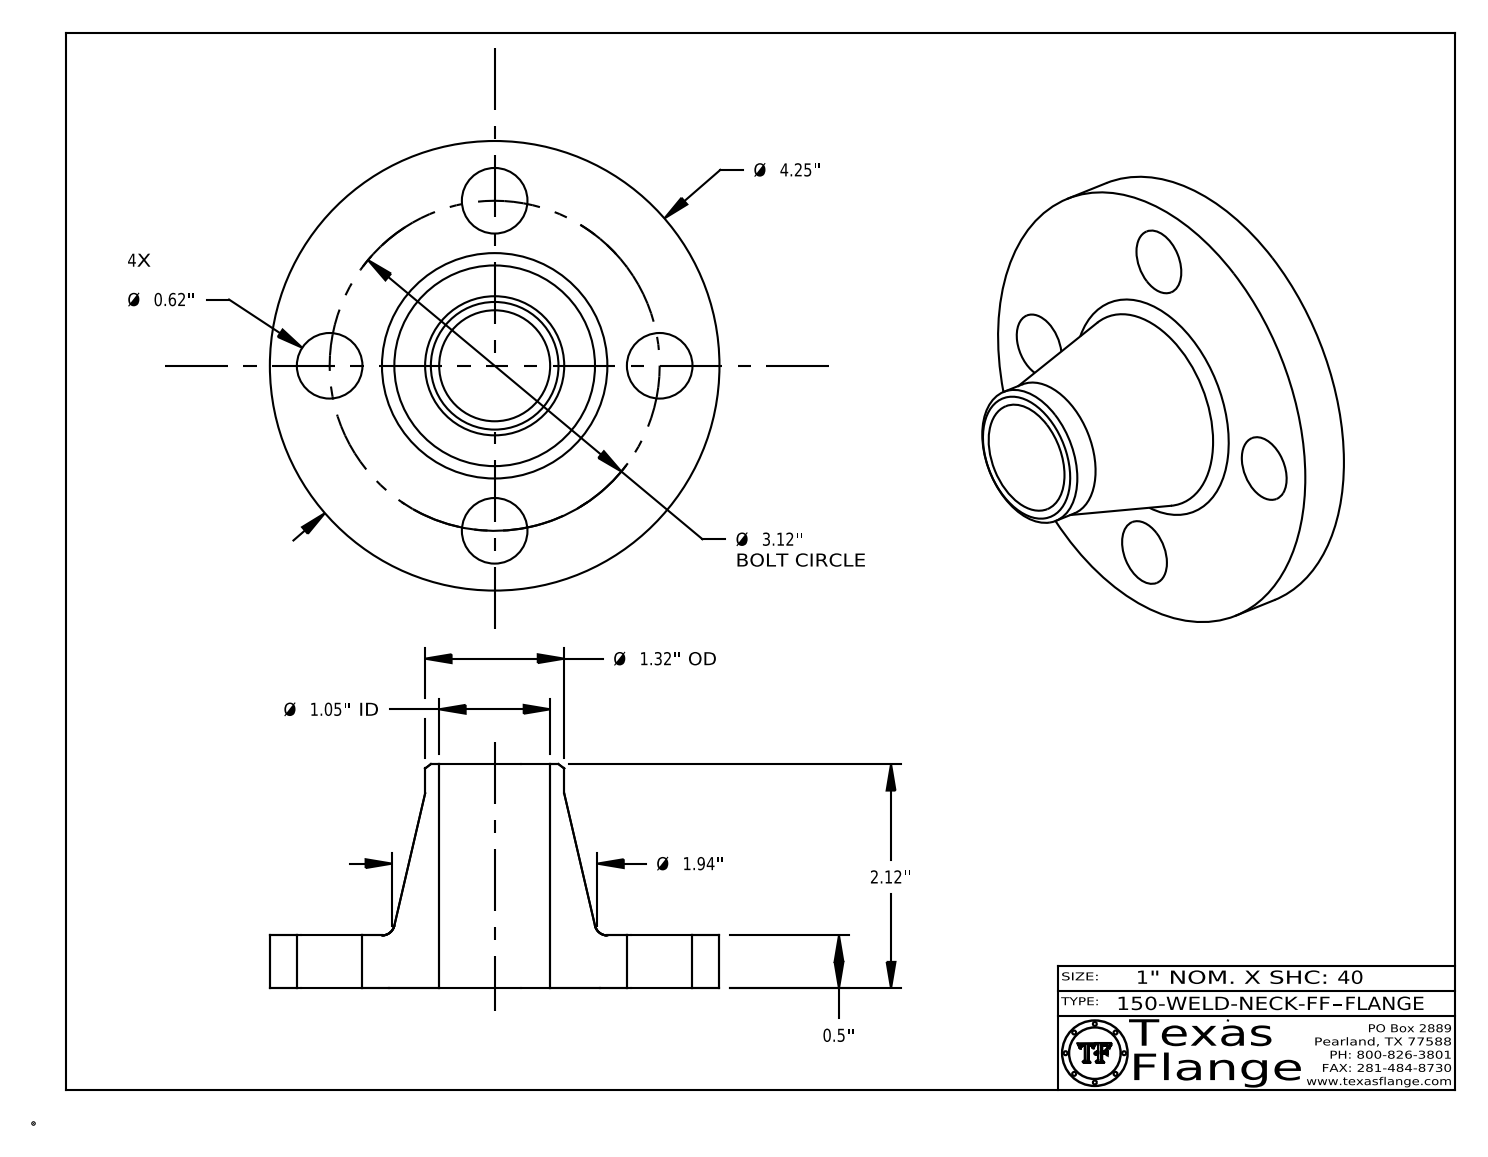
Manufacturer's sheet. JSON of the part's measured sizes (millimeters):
{"part_name": "150-WELD-NECK-FF", "step_written_by": "CATIA V5 STEP AP214 (AUTOMOTIVE_DESIGN)", "units": "millimeters", "bodies": {"solids": 1, "faces": 409, "planar": 369, "cylindrical": 34, "other": 6}, "overall_size": [108, 108, 53.8], "volume_mm3": 128900, "surface_area_mm2": 31080, "round_holes": [[15.7, 4], [12.6, 1], [26.6, 1]], "round_bosses_or_shafts": [[0.8, 8], [108, 1], [33.4, 1], [9.9, 1]], "face_to_face_distances": [12.7, 53.8, 41.1, 12.3, 0.4, 41.5, 3.8, 3.7, 0.7, 2.4], "hole_center_spacings": [39.6, 56, 30.3, 73.2, 79.2, 39.6]}
